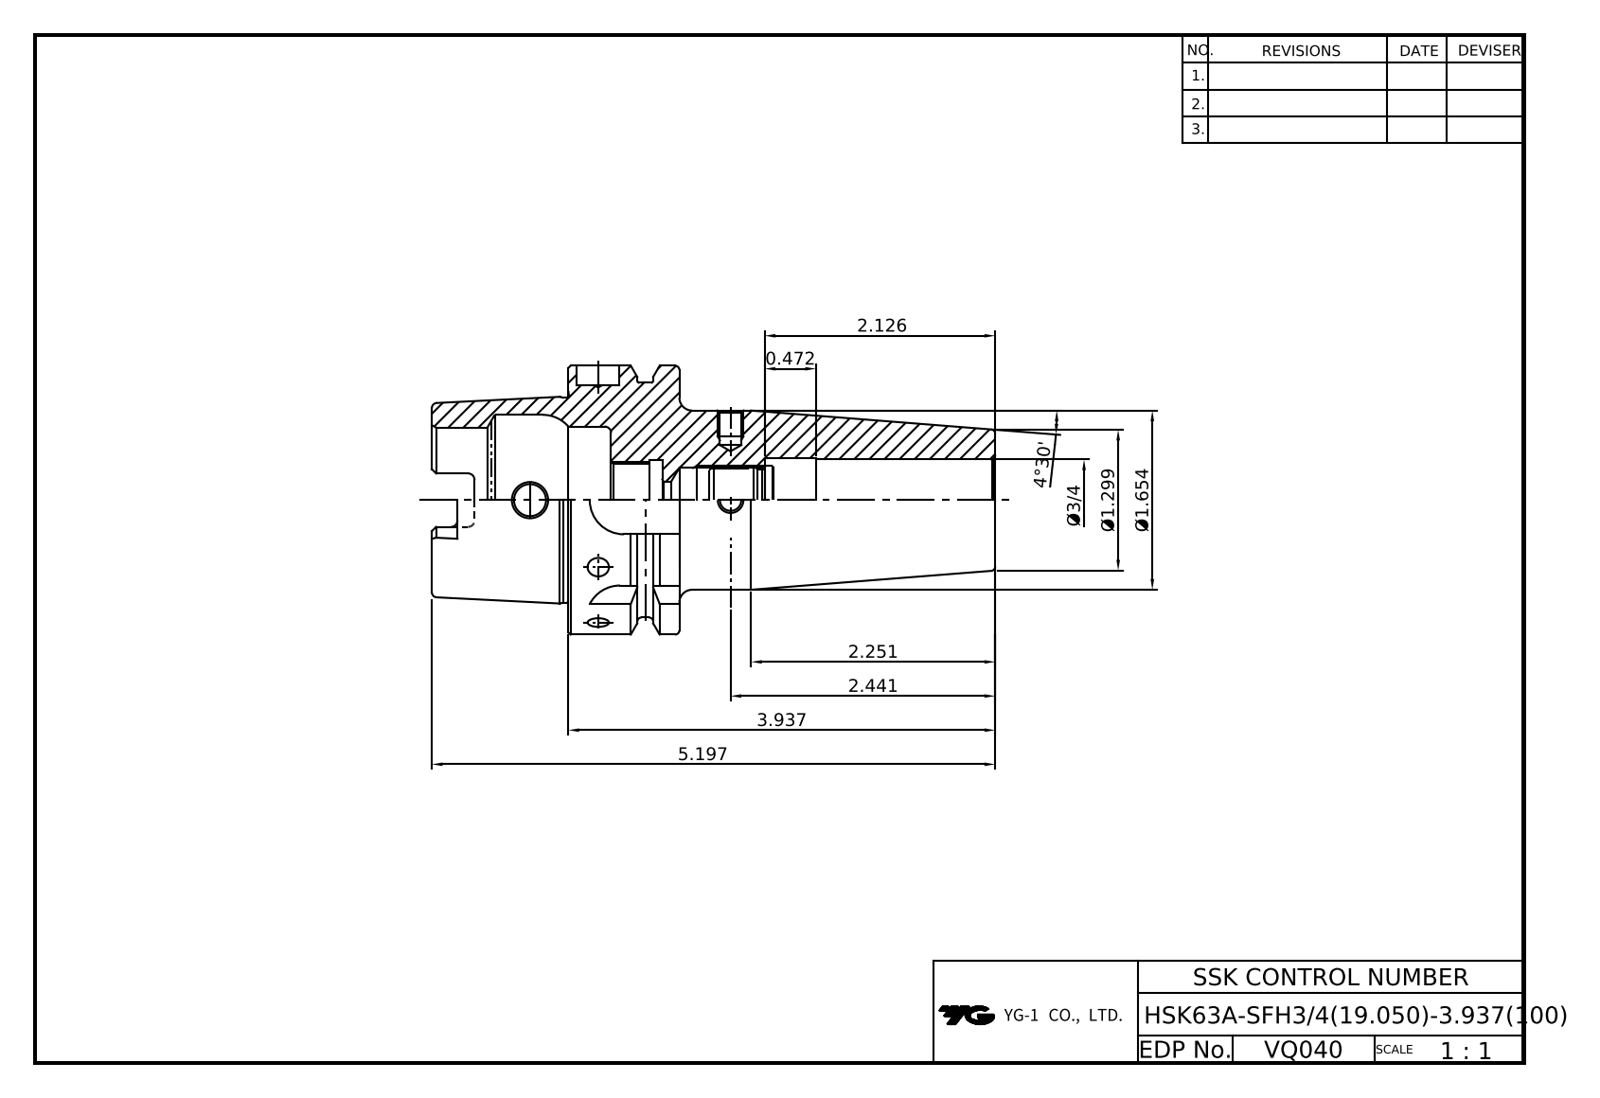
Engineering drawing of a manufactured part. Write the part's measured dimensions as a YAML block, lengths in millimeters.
part_name: "LO-HSK63A-SFH19.05-100"
step_written_by: "Autodesk Inventor 2022 (AUTOMOTIVE_DESIGN)"
units: millimeters
bodies: {solids: 1, faces: 116, planar: 42, cylindrical: 34, other: 40}
overall_size: [132, 63, 63]
volume: 149013
surface_area: 34776
round_holes:
  - {diameter: 7.5, count: 1}
  - {diameter: 8.4, count: 1}
  - {diameter: 10, count: 1}
  - {diameter: 14.92, count: 1}
  - {diameter: 16.92, count: 1}
  - {diameter: 19, count: 1}
  - {diameter: 19.05, count: 1}
  - {diameter: 20.25, count: 1}
  - {diameter: 34, count: 1}
  - {diameter: 40, count: 1}
round_bosses_or_shafts:
  - {diameter: 63, count: 1}
  - {diameter: 55, count: 1}
  - {diameter: 48.04, count: 1}
  - {diameter: 42, count: 1}
partial_cylinders:
  - {radius: 1.5, count: 6}
  - {radius: 2.88, count: 4}
  - {radius: 8, count: 4}
face_to_face_distances: [26, 10, 16, 90, 32, 100, 74, 42, 58, 54]
